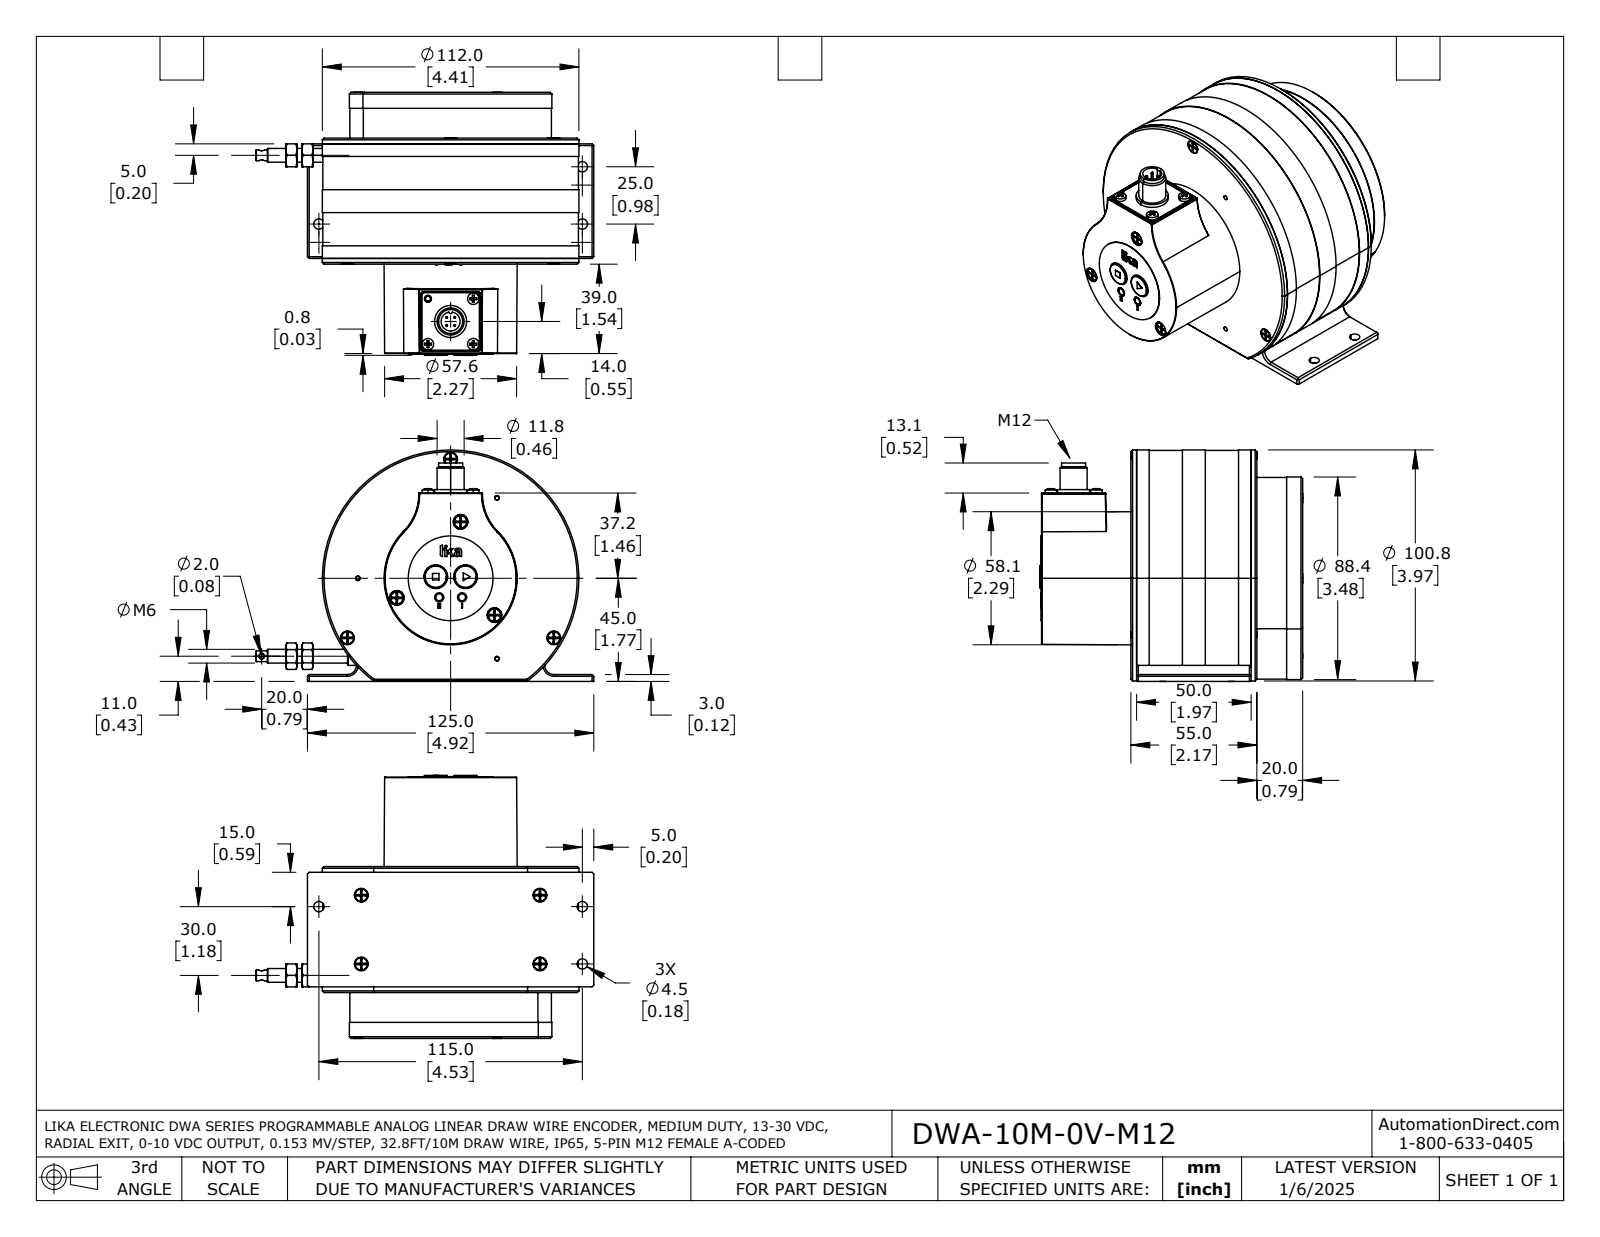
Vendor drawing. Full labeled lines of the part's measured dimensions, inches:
Part name (STEP PRODUCT): DWA-10M-0V-M12
STEP written by: SolidWorks 2021 (AUTOMOTIVE_DESIGN)
Units: inches
Bodies: 34 solids, 2254 faces (1254 planar, 476 cylindrical, 524 other)
Overall size (bounding box): 5.807 × 4.519 × 3.976
Volume: 16.69 in³ · Surface area: 228.9 in²
Round holes (diameter × count): ⌀0.098 ×13, ⌀0.126 ×7, ⌀0.236 ×7, ⌀0.157 ×4, ⌀0.177 ×4, ⌀0.197 ×4, ⌀0.081 ×3, ⌀0.11 ×3, ⌀0.059 ×2, ⌀0.063 ×2, ⌀0.079 ×2, ⌀0.118 ×2
Round bosses / shafts (diameter × count): ⌀0.118 ×11, ⌀0.098 ×6, ⌀0.055 ×4, ⌀0.031 ×4, ⌀0.197 ×3, ⌀0.157 ×2, ⌀4.409 ×1, ⌀3.48 ×1
Partial cylindrical surfaces — rounded edges, fillets, slot ends (radius × count): R0.008 ×44, R0.007 ×42, R0.02 ×6, R0.03 ×5, R0.157 ×2, R0.034 ×1, R0.035 ×1, R0.036 ×1
Main face-to-face distances: 0.079, 0.787, 0.02, 0.098, 0.807, 2.067, 2.953, 0.059, 2.146, 2.165
Hole centre spacings: 0.984, 1.705, 0.648, 0.728, 0.509, 1.039, 1.091, 1.224
